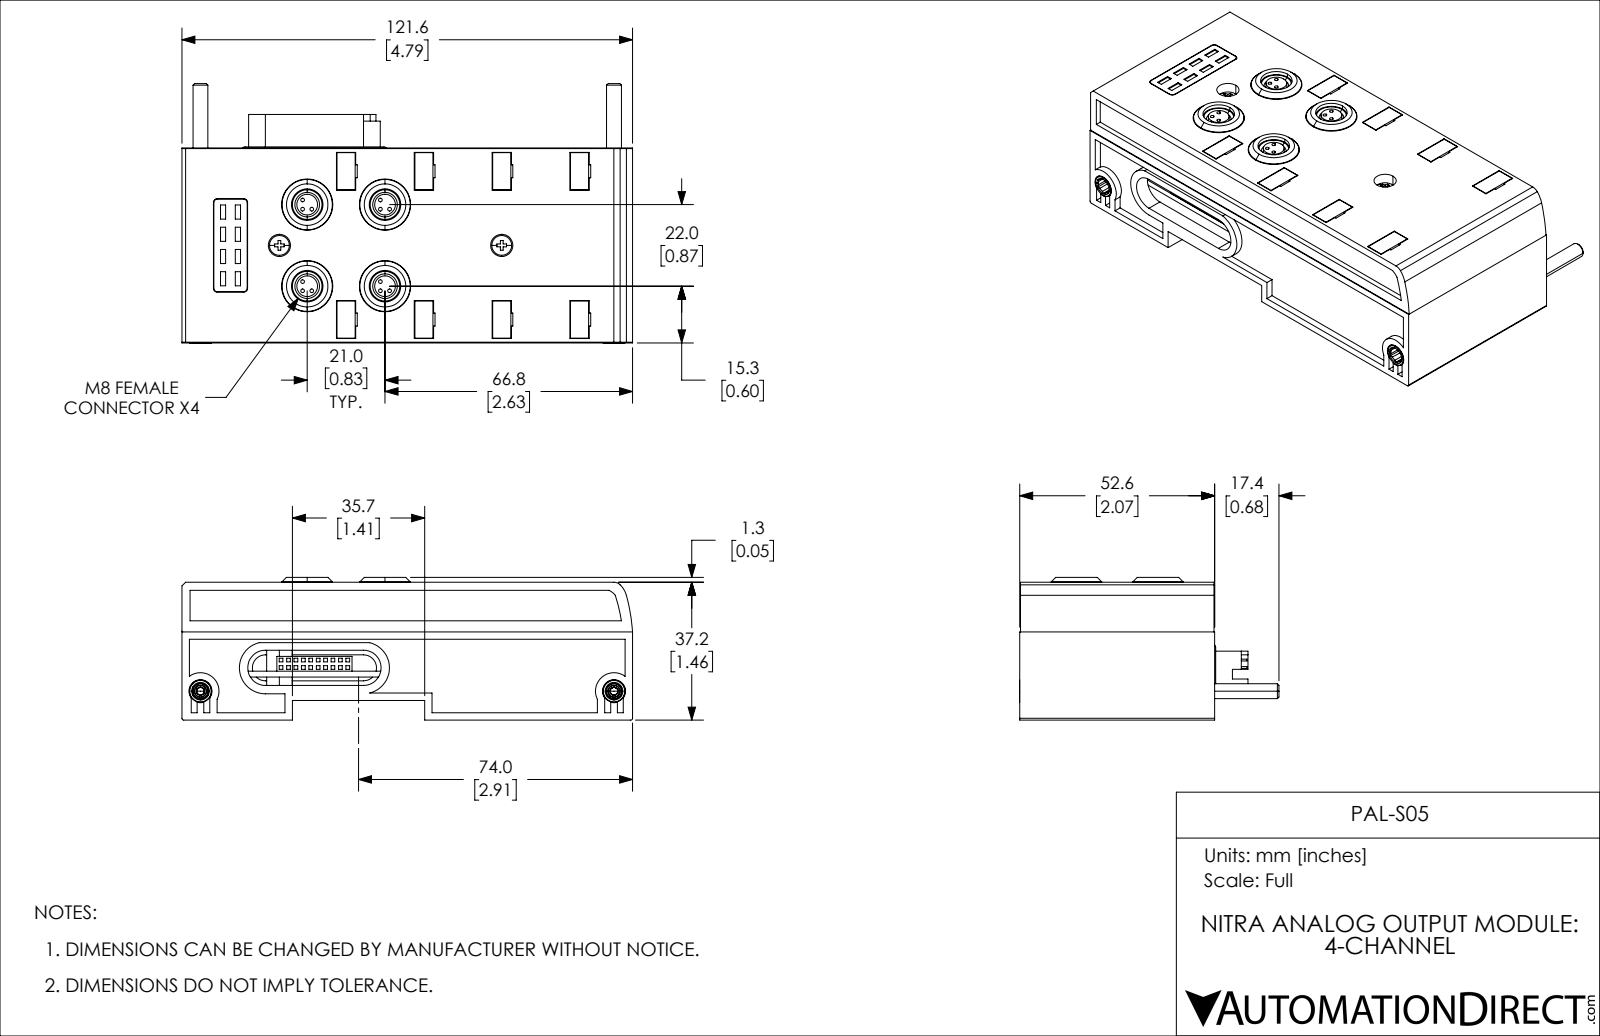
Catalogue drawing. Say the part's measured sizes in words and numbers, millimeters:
The part is named "PAL-S05". Its 3-D file was written by "SolidWorks 2019 (CONFIG_CONTROL_DESIGN)". It is 5 solids with 898 faces: 644 planar, 160 cylindrical and 94 other. Overall it measures 121.6 by 70 by 38.5 millimeters. Its volume is 145 400 cubic millimeters and its surface area 62 740 square millimeters. Round holes: 12 of diameter 1, 4 of diameter 6.7, 4 of diameter 8.5, 4 of diameter 13.8, 2 of diameter 3.3, 2 of diameter 6, 2 of diameter 6.2. Round bosses or shafts: 4 of diameter 13.6, 4 of diameter 5.6, 2 of diameter 6.9, 2 of diameter 6, 2 of diameter 5.4, 2 of diameter 4. Partial cylindrical surfaces (rounded edges, fillets, slot ends): 8 of radius 1, 2 of radius 0.5, 2 of radius 0.9, 2 of radius 2, 2 of radius 2.1, 2 of radius 3.5, 2 of radius 4.5, 2 of radius 4.7. The main face-to-face distances are 13.4, 8, 1.6, 13.2, 23.8, 37.2, 15.8, 29.2, 10.6, 5.2. The hole center spacings are 1.8, 2.5, 21, 22, 30.4, 19.8, 20.8, 22.3.
